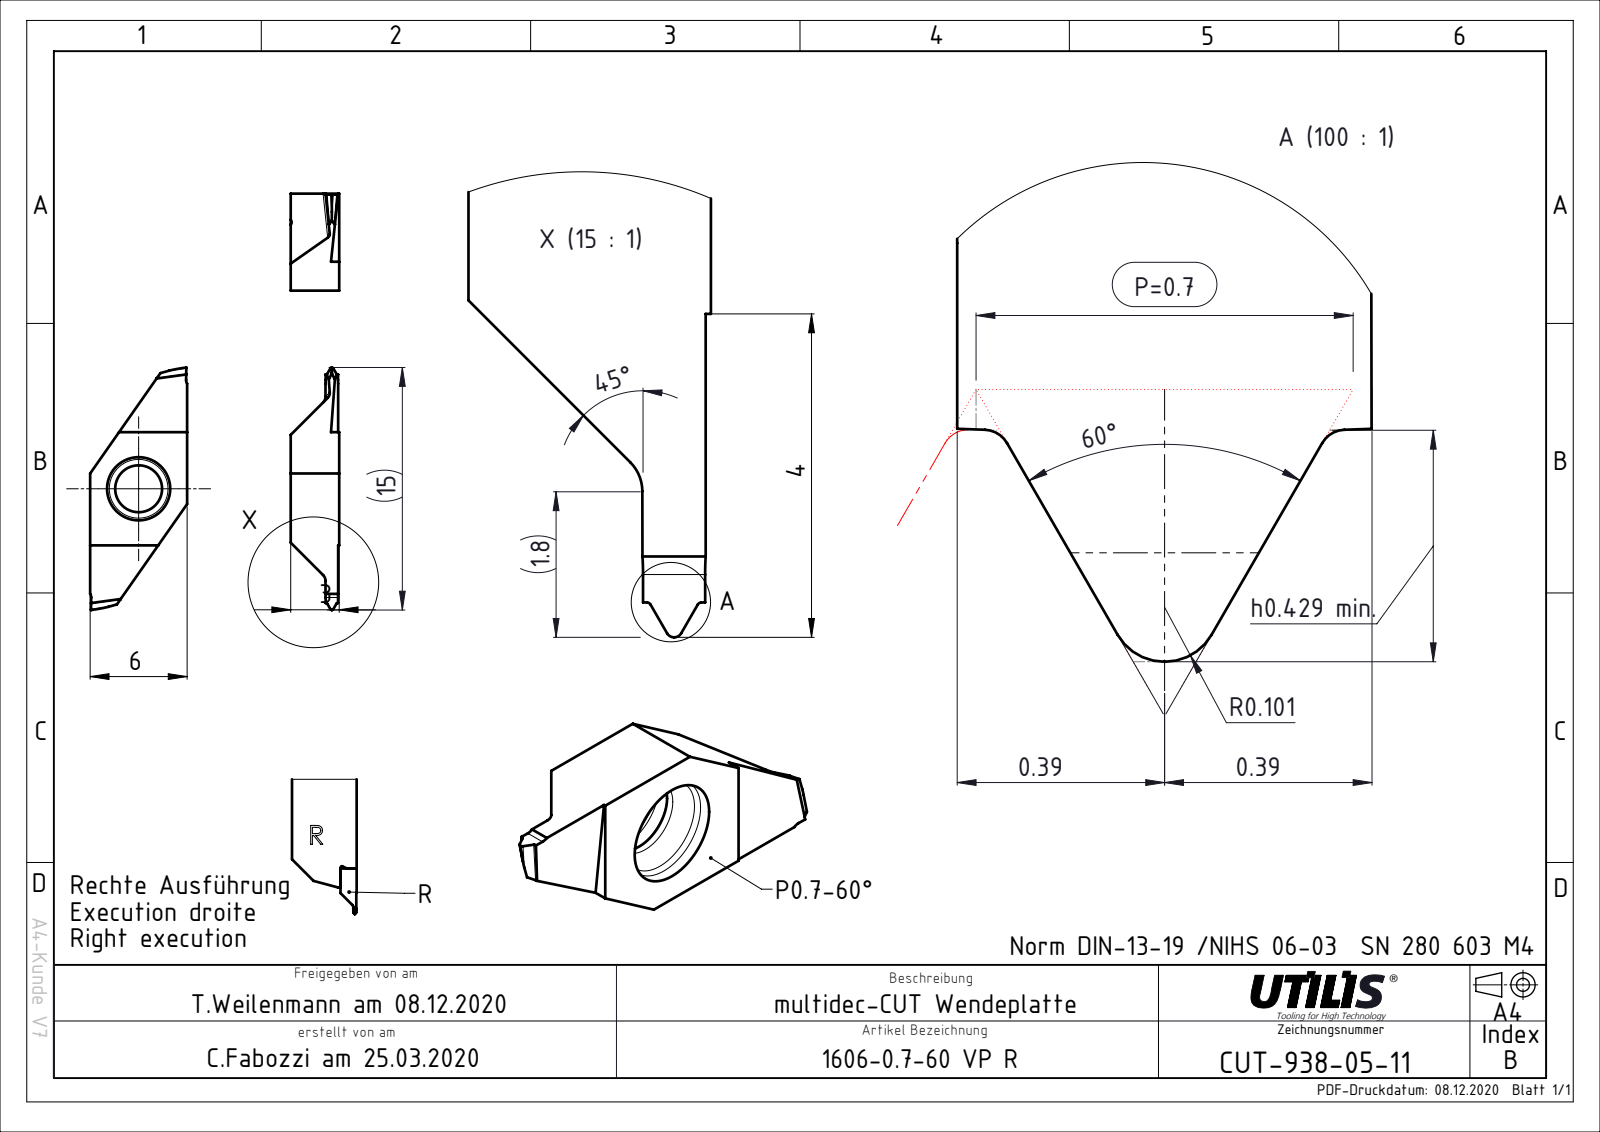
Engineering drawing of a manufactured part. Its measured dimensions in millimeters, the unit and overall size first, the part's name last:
Units: millimetres
Overall size (bounding box): 15 × 6 × 3
Round holes (diameter × count): ⌀2.9 ×1
Partial cylindrical surfaces — rounded edges, fillets, slot ends (radius × count): R0.1 ×4, R0.5 ×2
Main face-to-face distances: 6, 3, 0.62, 11.21, 9, 12, 7, 12.68
Volume: 123 mm³ · Surface area: 209 mm²
Bodies: 1 solid, 42 faces (24 planar, 14 cylindrical, 4 other)
Part name (STEP PRODUCT): CUT-938-05; ASME Y14.5
STEP written by: FormatWorks Professional (AP242_MANAGED_MODEL_BASED_3D_ENGINEERING_MIM_LF)
